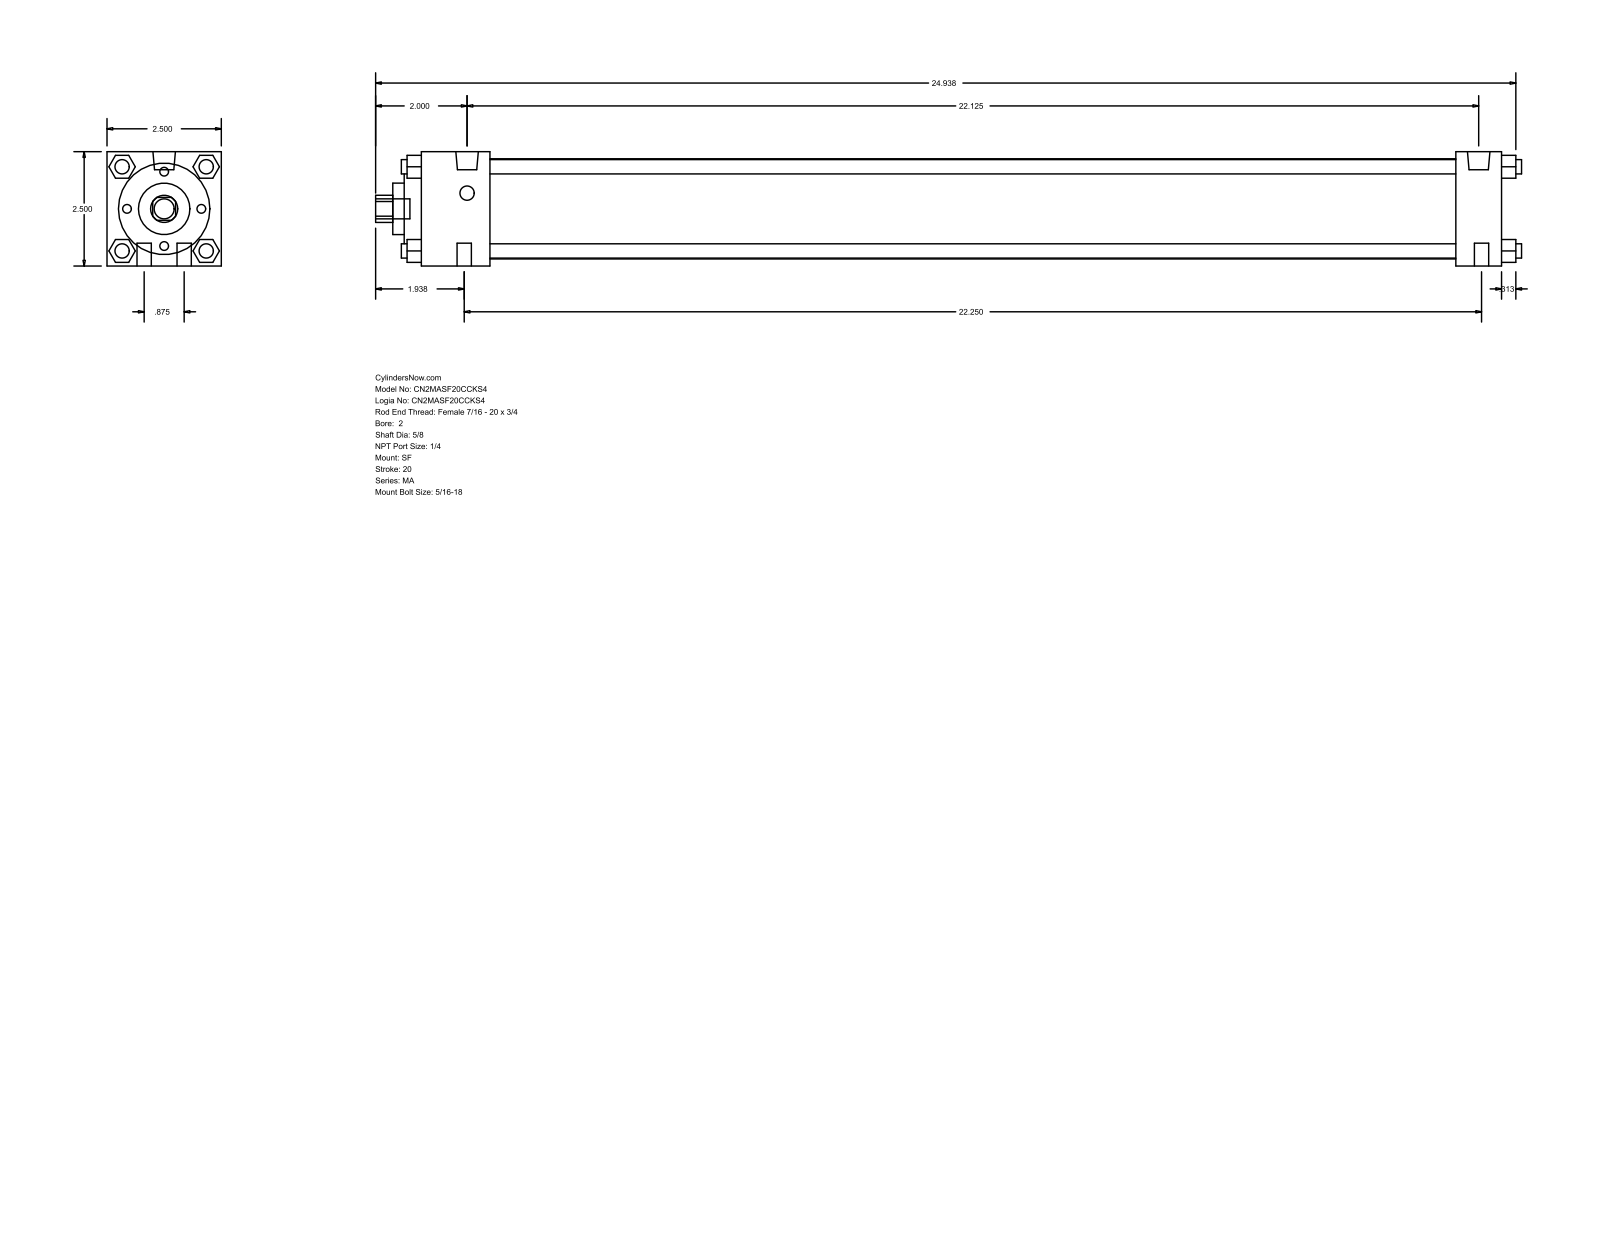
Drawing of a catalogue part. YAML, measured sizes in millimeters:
part_name: "MA_SF__0200_0.625"
step_written_by: "GSSL Pune (CONFIG_CONTROL_DESIGN)"
units: millimeters
bodies: {solids: 0, faces: 126, planar: 95, cylindrical: 31, other: 0}
overall_size: [636.59, 63.5, 63.5]
round_holes:
  - {diameter: 15.88, count: 1}
  - {diameter: 28.57, count: 1}
  - {diameter: 50.8, count: 1}
  - {diameter: 55.63, count: 1}
round_bosses_or_shafts:
  - {diameter: 7.94, count: 10}
  - {diameter: 12.49, count: 2}
  - {diameter: 11.11, count: 1}
partial_cylinders:
  - {radius: 7.54, count: 1}
face_to_face_distances: [63.5, 12.7, 25.4, 38.1, 600.08, 9.52, 574.68, 536.58, 561.98, 47.62]
